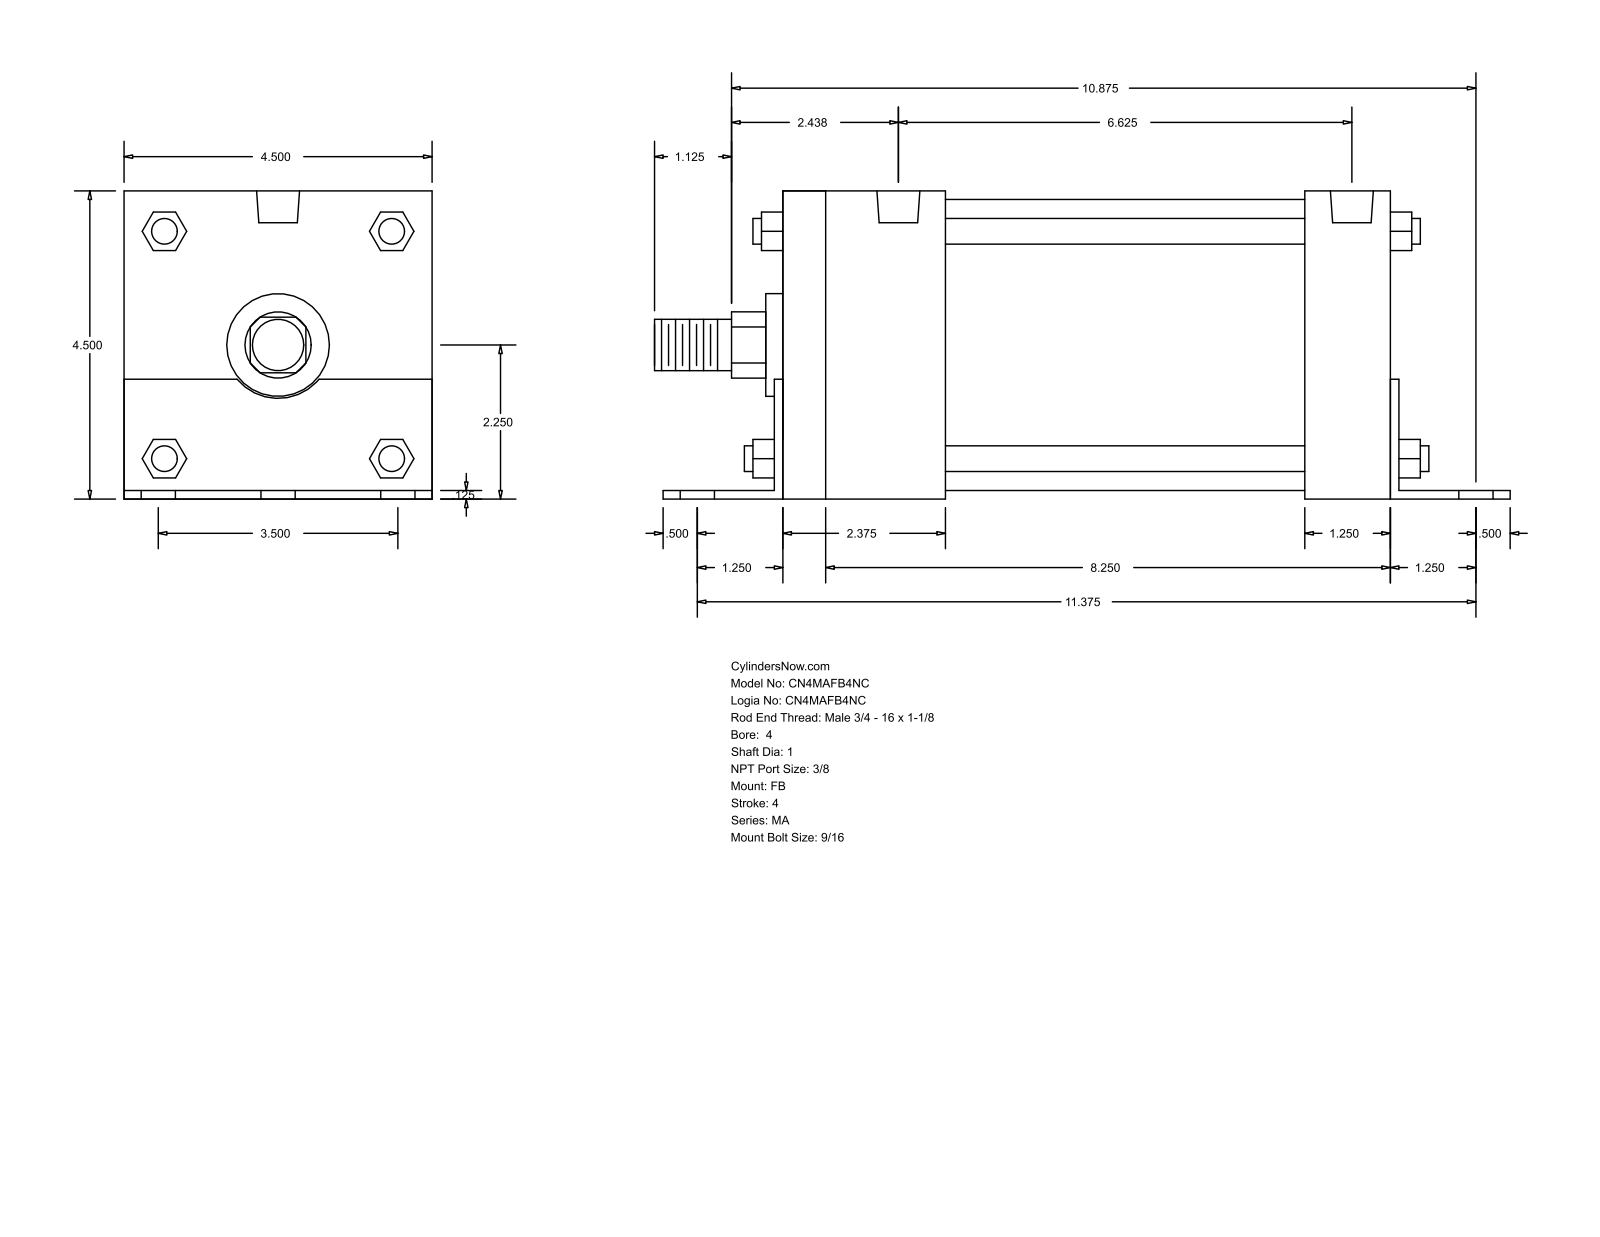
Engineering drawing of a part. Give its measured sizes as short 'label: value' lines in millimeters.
name: MA_FB__0400_1
written by: GSSL Pune (CONFIG_CONTROL_DESIGN)
unit: mm
bodies: 0 solids, 140 faces (105 planar, 35 cylindrical, 0 other)
size: 317.5 × 114.35 × 114.3
holes: 6× ⌀14.29, 4× ⌀11.11, 2× ⌀15.93
bosses: 4× ⌀9.53, 1× ⌀107.95, 1× ⌀38.1, 1× ⌀25.4, 1× ⌀19.05
rounds: 1× R12.29, 1× R19.81
face distances: 114.3, 3.17, 114.35, 3.12, 111.18, 225.42, 3.18, 231.77, 228.6, 228.59
hole spacings: 44.45, 292.33, 288.93, 4.76, 64, 67.5, 86.85, 88.9
